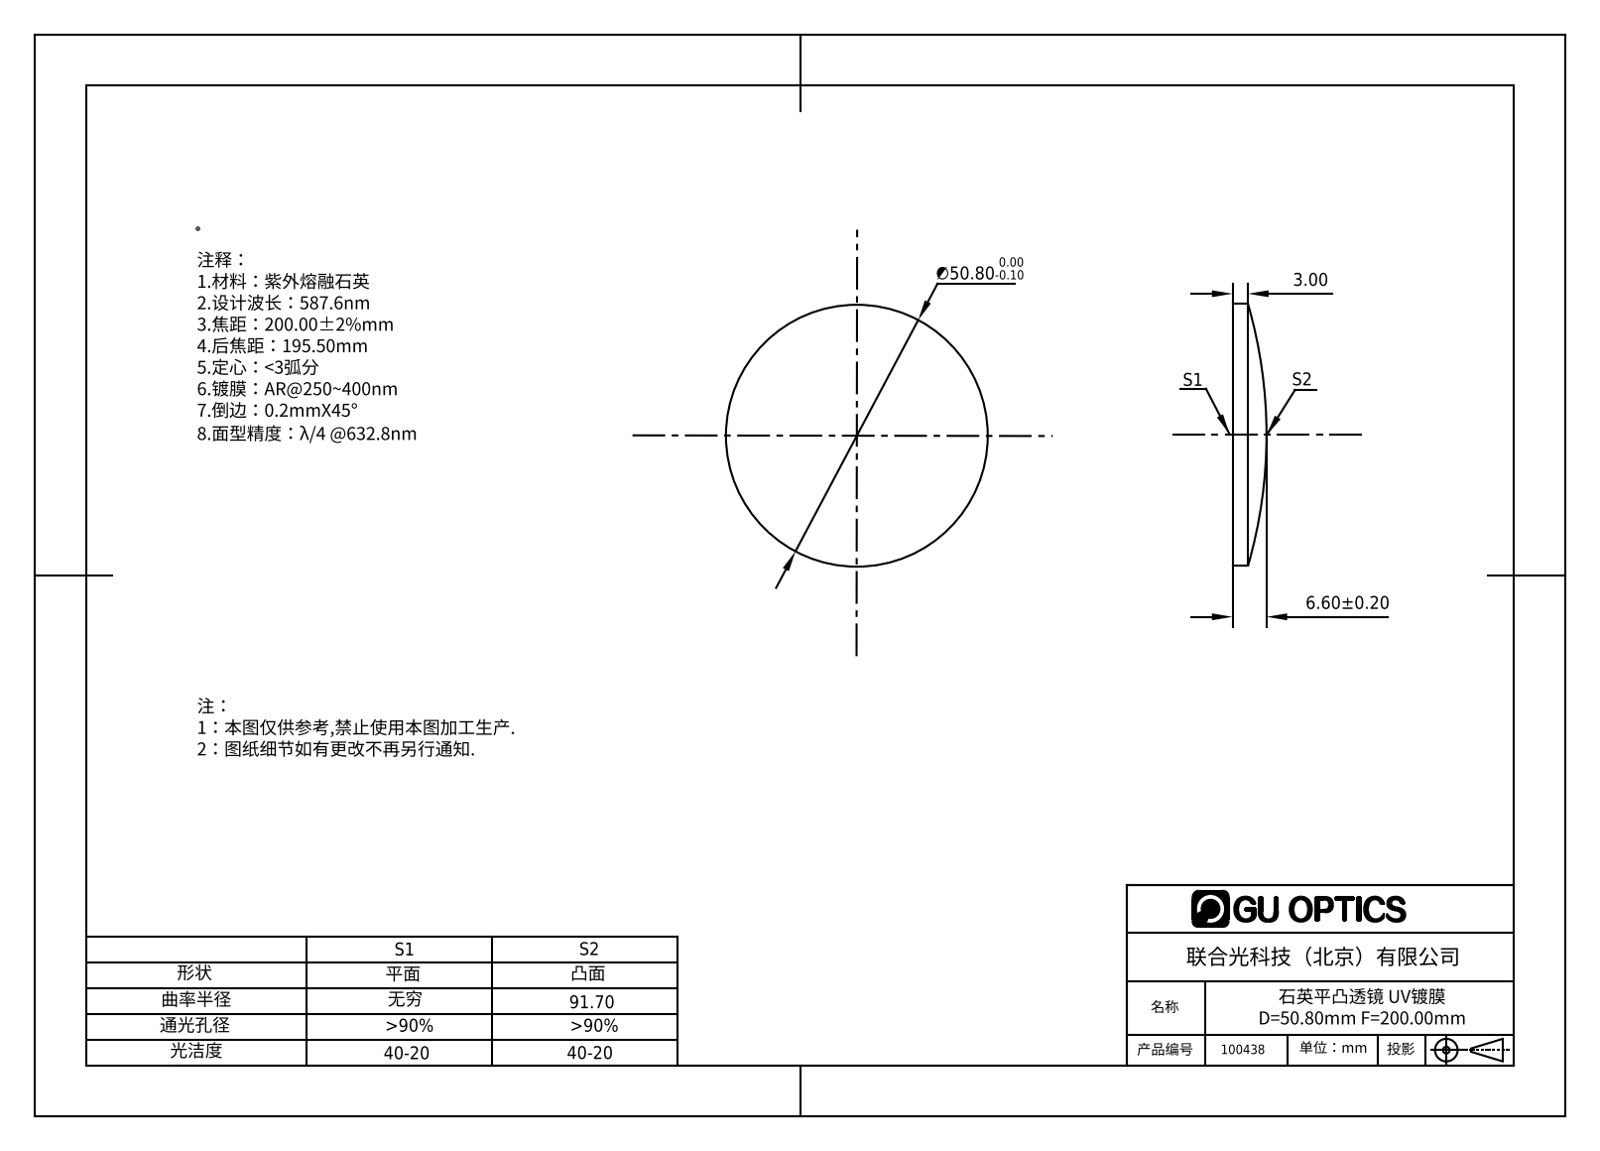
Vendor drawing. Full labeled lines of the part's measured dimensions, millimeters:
Part name (STEP PRODUCT): 100388
STEP written by: SolidWorks 2016 (AUTOMOTIVE_DESIGN)
Units: millimetres
Bodies: 1 solid, 5 faces (1 planar, 2 cylindrical, 2 other)
Overall size (bounding box): 50.8 × 50.8 × 6.6
Volume: 9 753 mm³ · Surface area: 4 573 mm²
Round bosses / shafts (diameter × count): ⌀50.8 ×1
